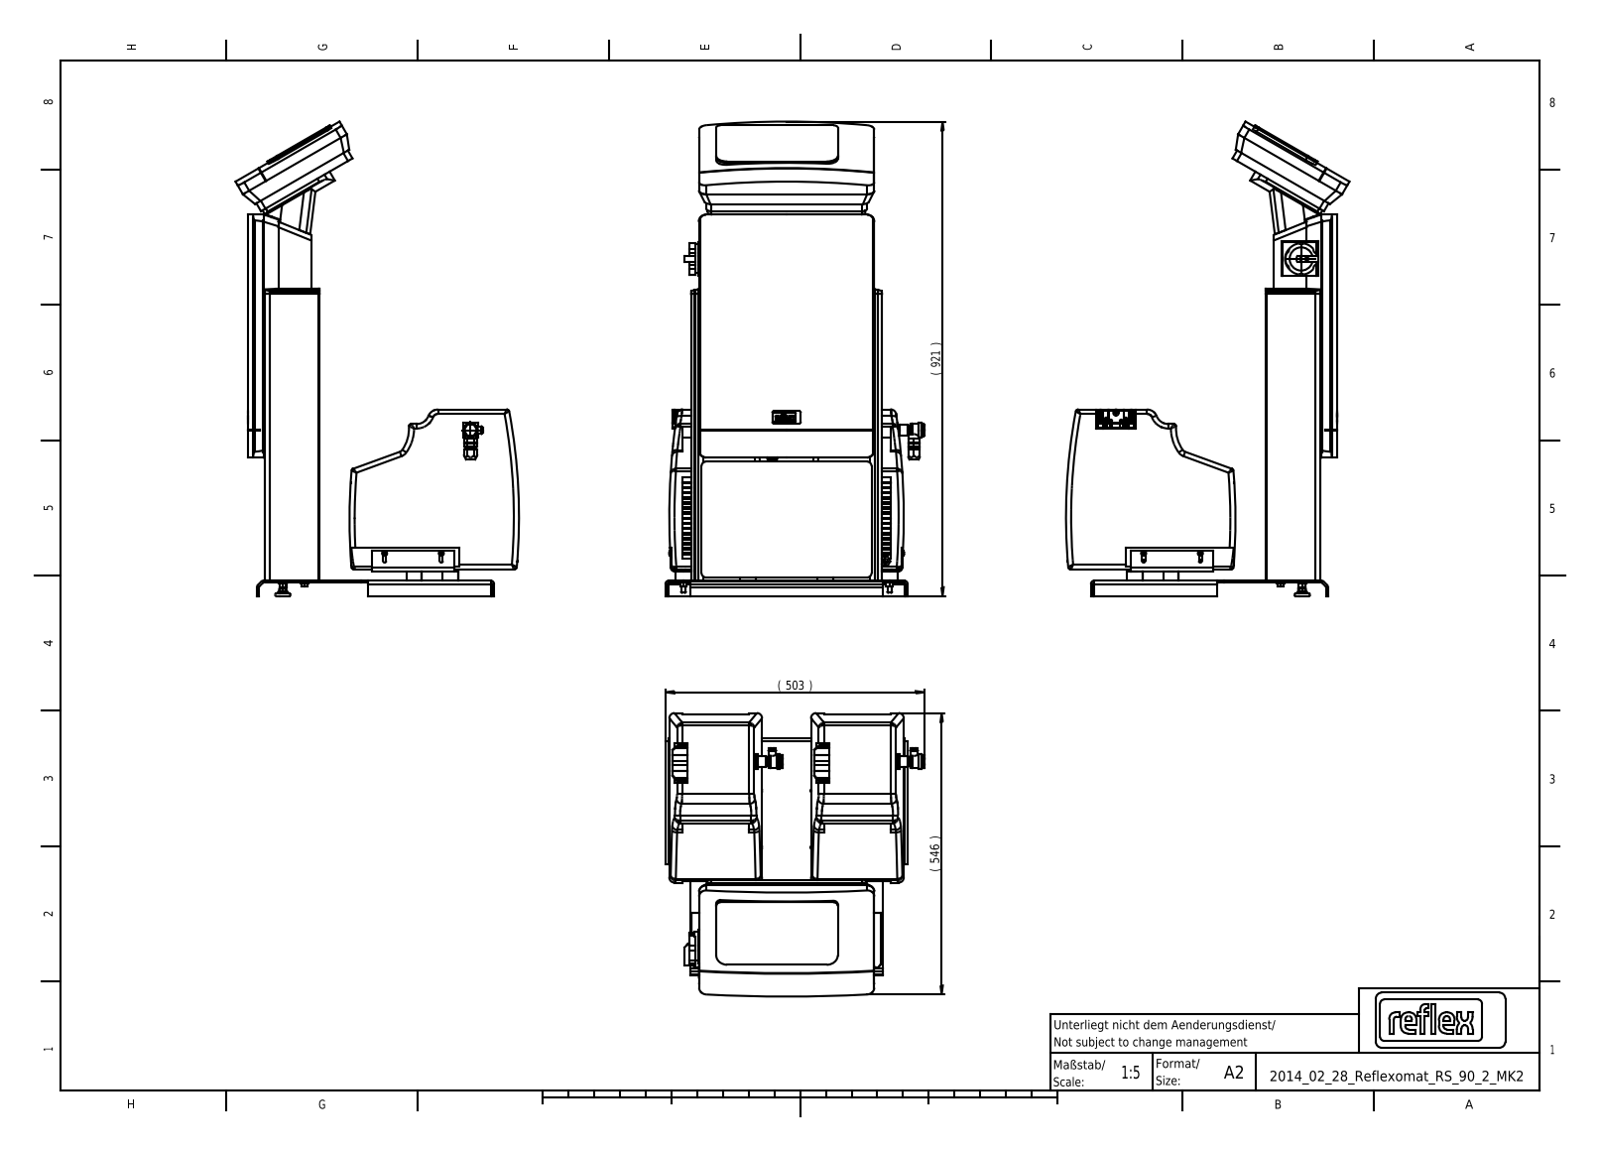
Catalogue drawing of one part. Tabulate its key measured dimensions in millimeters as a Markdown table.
| quantity | value |
| --- | --- |
| STEP written by | Mechanical Desktop 2011 (CONFIG_CONTROL_DESIGN) |
| units | millimeters |
| bodies | 95 solids, 4604 faces (2872 planar, 782 cylindrical, 950 other) |
| overall size | 920.68 × 550.06 × 502.91 |
| volume | 55 260 000 mm³ |
| surface area | 3 771 000 mm² |
| round holes (diameter × count) | 9 × 20, 8.2 × 16, 17.5 × 13, 10.5 × 9, 17 × 8, 5.5 × 6, 13.5 × 4, 5.4 × 3, 20.5 × 3, 6.5 × 2, 10 × 2, 14 × 2 |
| round bosses / shafts (diameter × count) | 20 × 12, 16 × 12, 8 × 12, 11.2 × 9, 5.1 × 9, 30 × 8, 19 × 8, 17.5 × 8 |
| partial cylindrical surfaces (radius × count) | 3 × 29, 10 × 23, 5 × 13, 2.5 × 9, 6.5 × 6, 7.5 × 6, 14 × 6, 1 × 5 |
| main face-to-face distances | 4, 22, 2, 26, 15, 24, 20, 92, 18, 77 |
| hole center spacings | 31, 62, 70, 125, 143.27, 148.09, 36, 93 |
